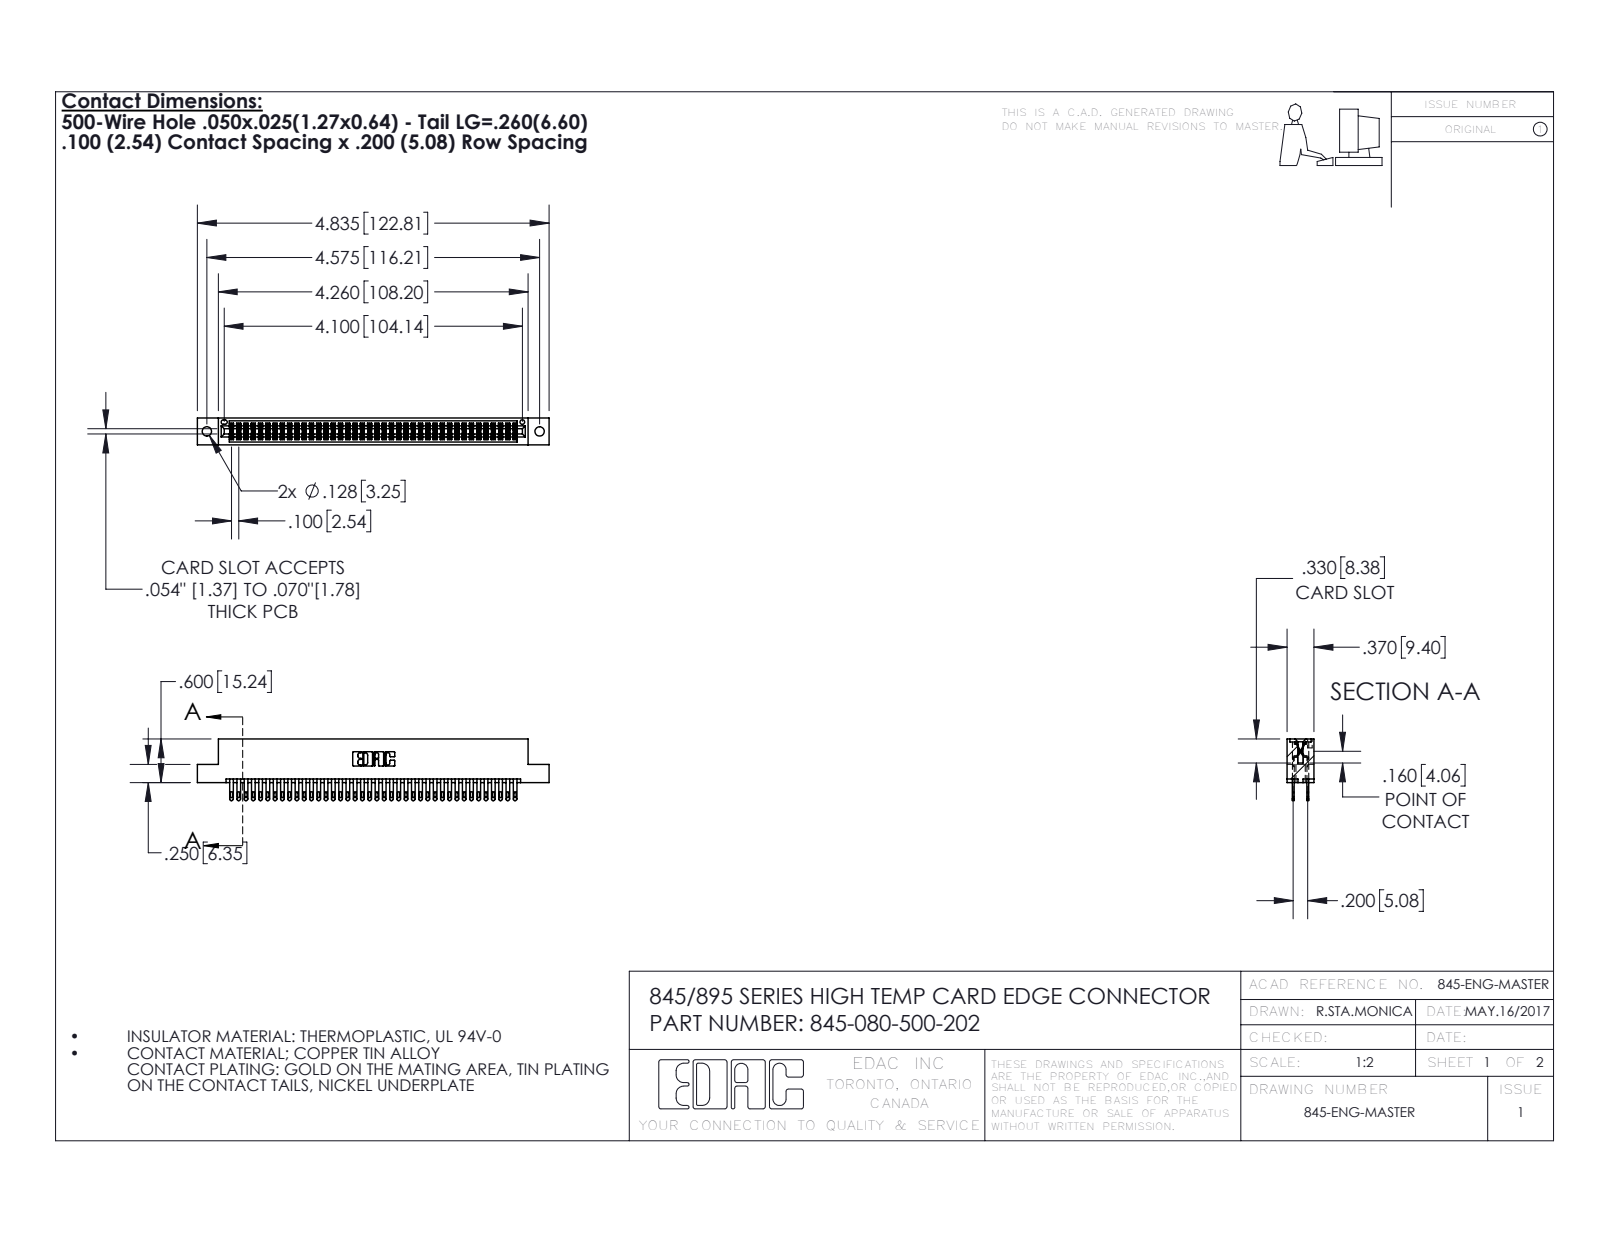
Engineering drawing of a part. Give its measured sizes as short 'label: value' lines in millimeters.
name: 345-080-500-202; 345 Part_Flush Mounting Lugs - 0.128 Dia; 345-292-001_345-293-100
written by: SolidWorks 2016 (CONFIG_CONTROL_DESIGN)
unit: mm
bodies: 81 solids, 3806 faces (2240 planar, 1566 cylindrical, 0 other)
size: 122.8 × 21.5 × 9.4
volume: 12 100 mm³; area: 18 420 mm²
holes: 2× ⌀3.3, 1× ⌀1.6
rounds: 120× R0.2, 80× R0.4, 80× R0.5, 22× R0.3, 6× R0.2, 6× R0.8, 3× R0.7, 2× R0.4
face distances: 7.6, 1.8, 5.1, 2.5, 6.9, 0.6, 9.4, 5.7, 4.4, 3.8
hole spacings: 6.9, 110.2, 116.2
